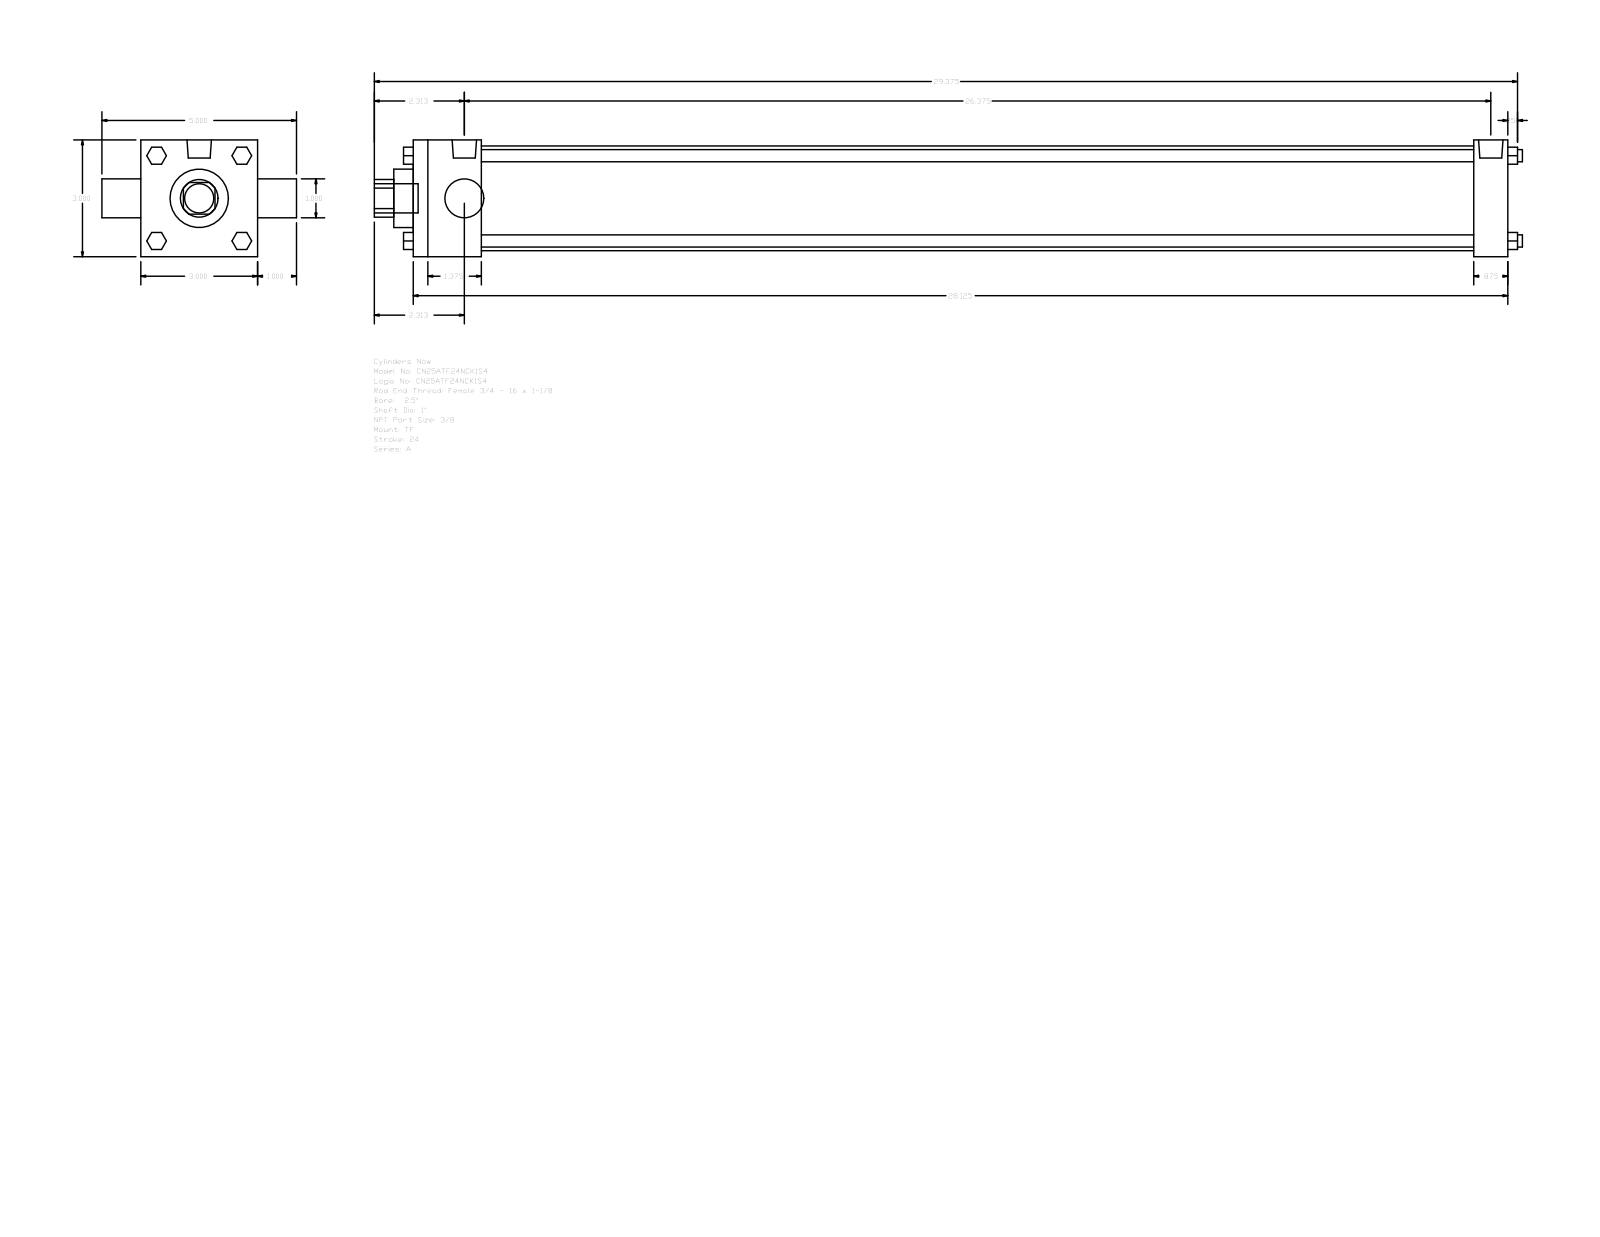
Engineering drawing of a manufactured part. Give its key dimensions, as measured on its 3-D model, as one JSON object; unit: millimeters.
{"part_name": "A_TF__0250_1", "step_written_by": "GSSL Pune (CONFIG_CONTROL_DESIGN)", "units": "millimeters", "bodies": {"solids": 0, "faces": 120, "planar": 92, "cylindrical": 28, "other": 0}, "overall_size": [749.3, 127, 76.2], "round_holes": [[25.4, 2], [38.1, 1], [68.33, 1]], "round_bosses_or_shafts": [[7.94, 4], [5.56, 3], [15.93, 2], [19.05, 1]], "partial_cylinders_radius": [[12.29, 1]], "face_to_face_distances": [76.2, 714.37, 44.45, 692.15, 647.7, 669.92, 22.22, 25.4, 101.6, 727.07]}
